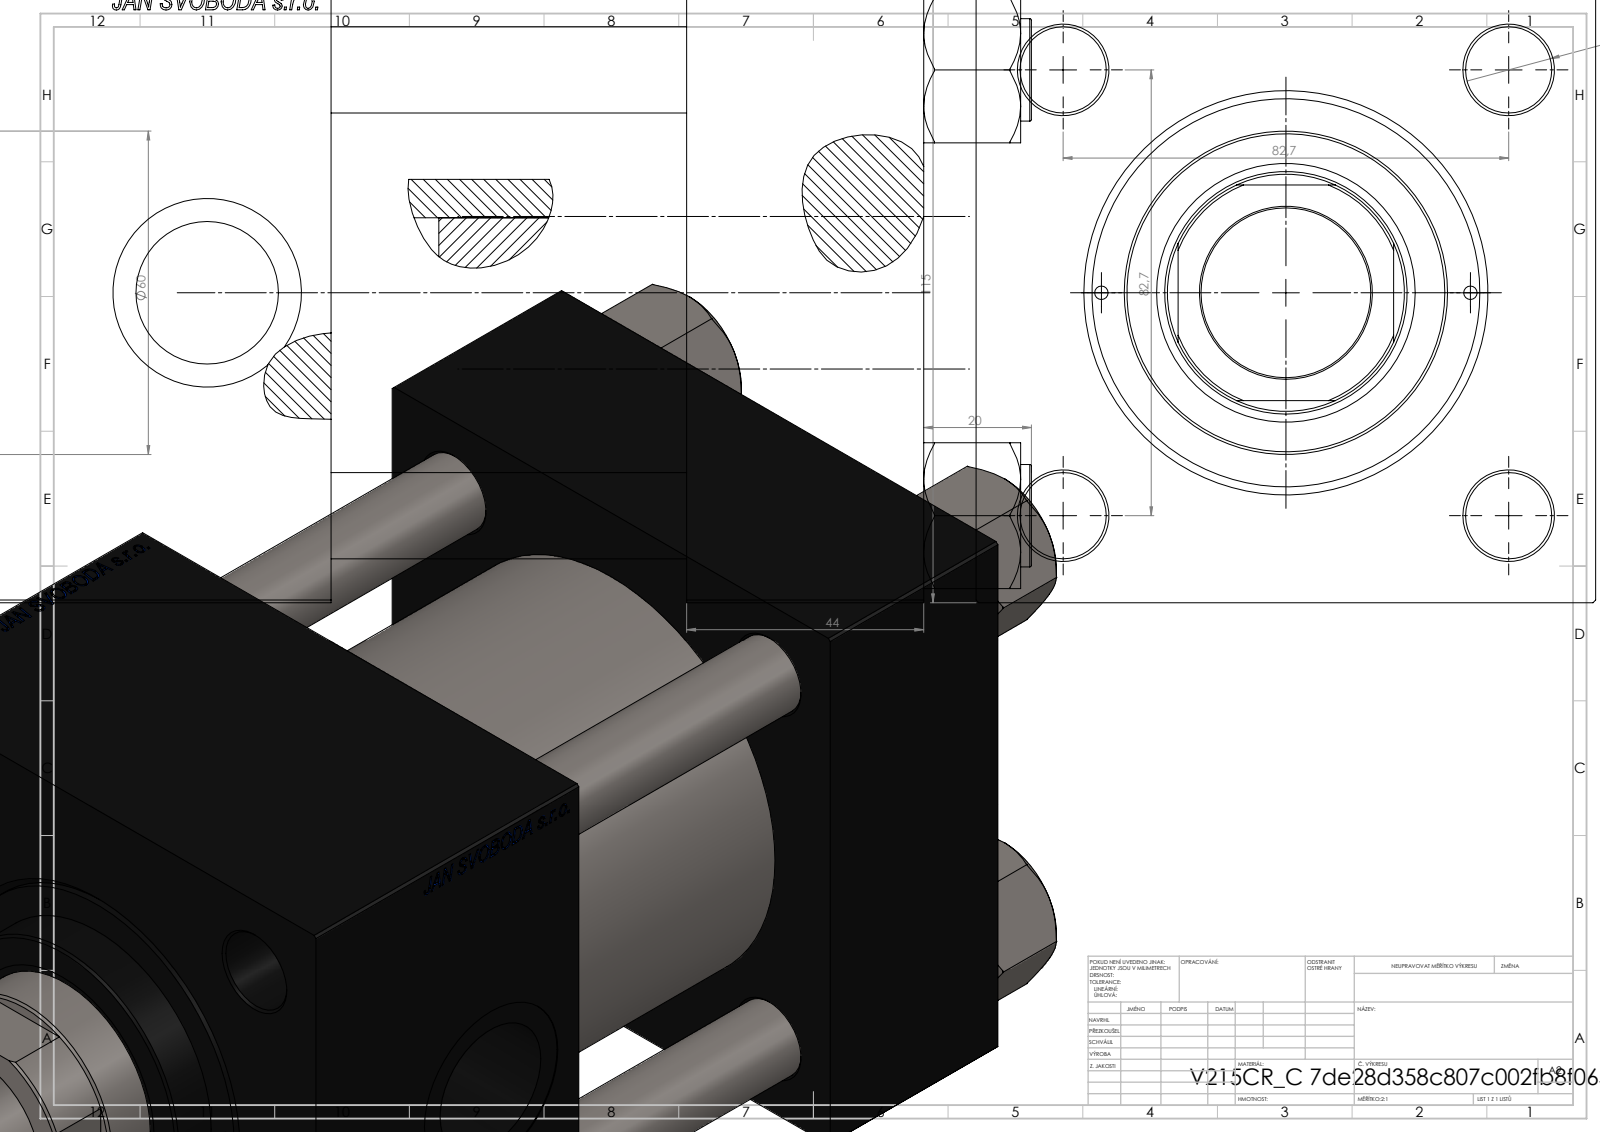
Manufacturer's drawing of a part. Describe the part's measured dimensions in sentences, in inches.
The part is named "NUT_M5_C; V215CR_C_TYCINKA; V215CR_C_Body; V215_VC_A (+1 more)". Its 3-D file was written by "SolidWorks 2019 (CONFIG_CONTROL_DESIGN)". It is 11 solids with 1202 faces: 576 planar, 90 cylindrical and 536 other. Overall it measures 9.055 by 4.528 by 4.528 inches. Its volume is 111 cubic inches and its surface area 424.6 square inches. Round holes: 4 of diameter 0.63, 2 of diameter 0.098, 2 of diameter 0.276, 2 of diameter 1.041, 2 of diameter 1.378, 1 of diameter 1.24, 1 of diameter 1.772, 1 of diameter 1.89, 1 of diameter 2.402, 1 of diameter 2.835, 1 of diameter 3.15. Round bosses or shafts: 4 of diameter 0.748, 1 of diameter 3.386, 1 of diameter 2.362. Partial cylindrical surfaces (rounded edges, fillets, slot ends): 1 of radius 0.866. The main face-to-face distances are 4.528, 1.732, 4.331, 7.047, 5.315, 2.598, 2.717, 0.787, 5.917, 4.185. The hole center spacings are 1.652, 2.302, 3.256, 3.393, 1.348, 4.605, 2.697, 4.37.
